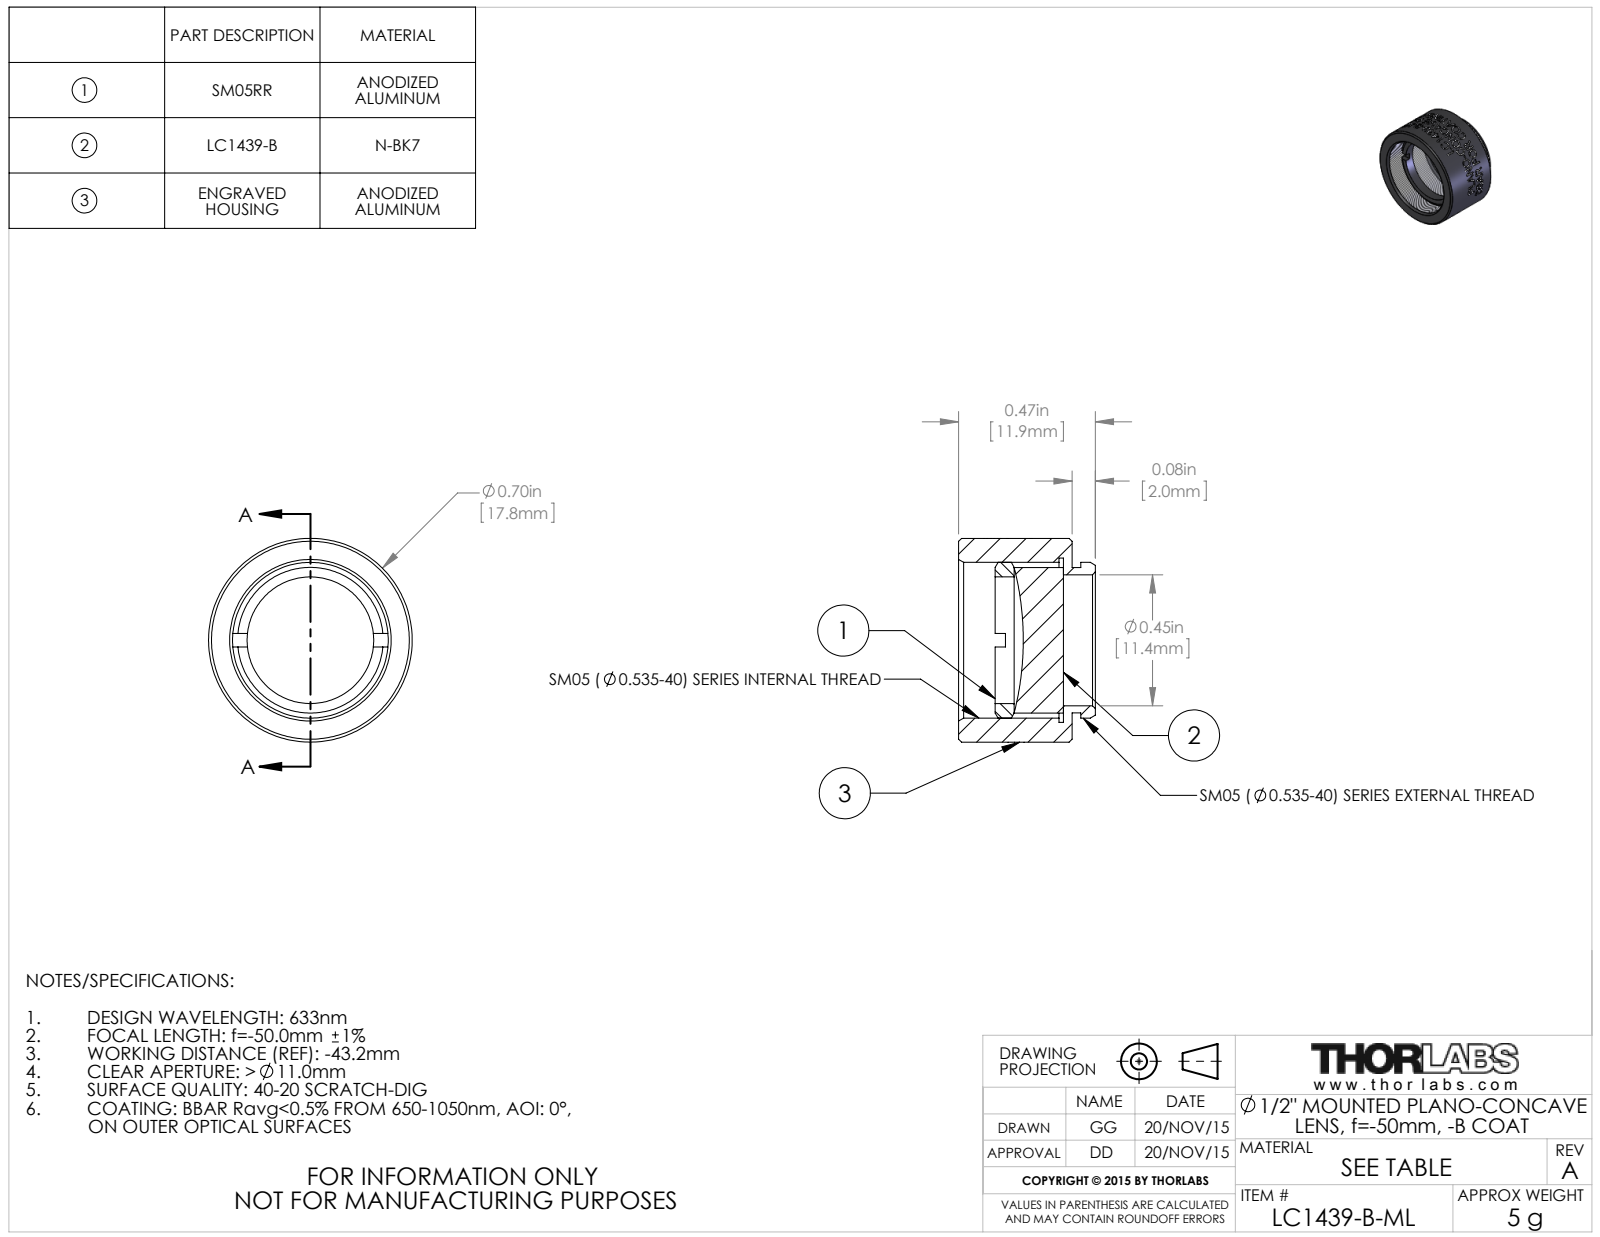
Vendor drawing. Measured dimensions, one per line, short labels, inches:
name: TTN045265-E0W
written by: SolidWorks 2014 (CONFIG_CONTROL_DESIGN)
unit: in
bodies: 3 solids, 152 faces (16 planar, 119 cylindrical, 17 other)
size: 0.7 × 0.7 × 0.47
volume: 0.102 in³; area: 3.242 in²
holes: 1× ⌀0.435, 1× ⌀0.45, 1× ⌀0.535, 1× ⌀0.565
bosses: 1× ⌀0.7, 1× ⌀0.535, 1× ⌀0.5, 1× ⌀0.499
face distances: 0.03, 0.39, 0.36, 0.199, 0.169, 0.191, 0.264, 0.234, 0.065, 0.126
